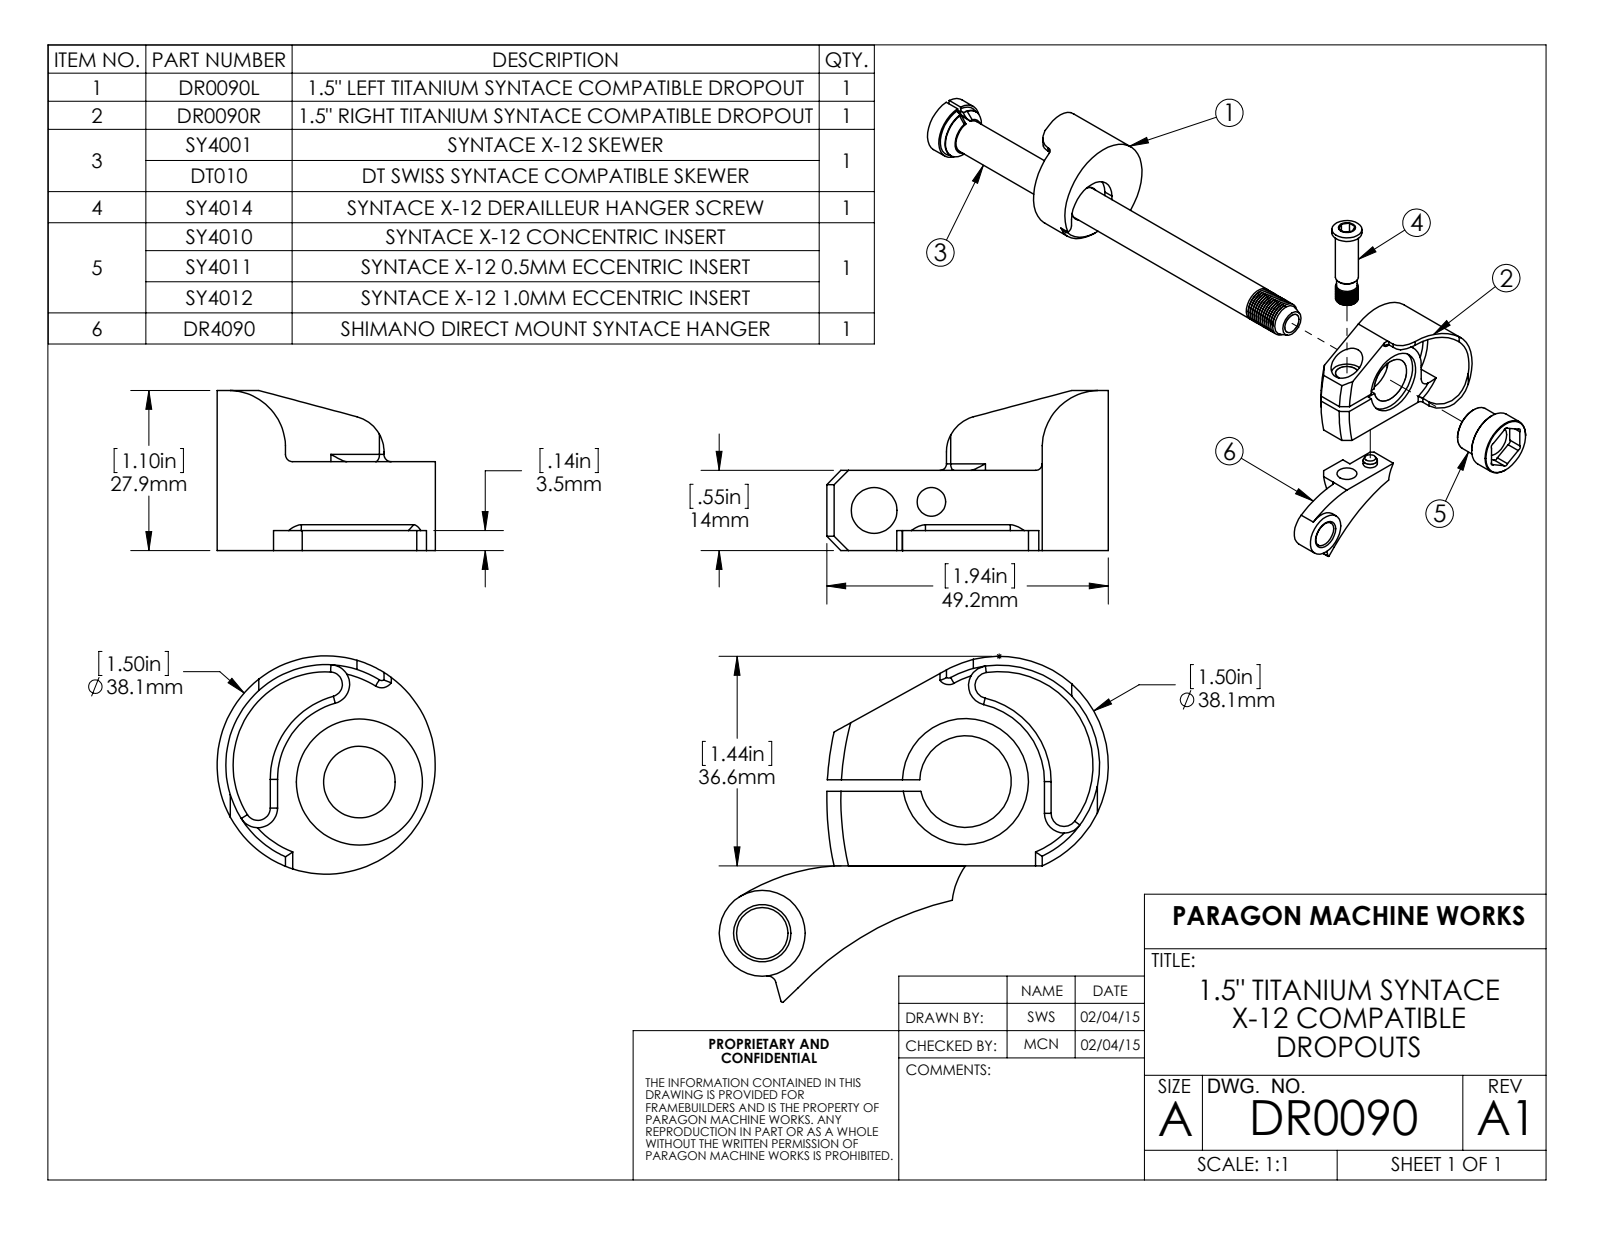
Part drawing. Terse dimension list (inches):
name: DR0090L_default; DR0090R; SY4014; SY4010 (+5 more)
written by: SolidWorks 2014 (AUTOMOTIVE_DESIGN)
unit: in
bodies: 8 solids, 364 faces (81 planar, 115 cylindrical, 168 other)
size: 7.515 × 2.674 × 2.384
volume: 2.878 in³; area: 50.14 in²
holes: 2× ⌀0.276, 2× ⌀0.433, 1× ⌀0.157, 1× ⌀0.197, 1× ⌀0.315, 1× ⌀0.354, 1× ⌀0.472, 1× ⌀0.492, 1× ⌀0.63, 1× ⌀0.866
bosses: 2× ⌀0.591, 1× ⌀1.5, 1× ⌀0.787, 1× ⌀0.697, 1× ⌀0.632, 1× ⌀0.606, 1× ⌀0.413, 1× ⌀0.285
rounds: 9× R0.039, 4× R0.135, 3× R0.045, 3× R0.05, 2× R0.03, 2× R0.098, 2× R0.197, 2× R0.25
face distances: 0.551, 0.138, 5.453, 0.177, 5.315, 5.866, 0.61, 5.925, 6.476, 0.315
hole spacings: 0.398, 1.743
